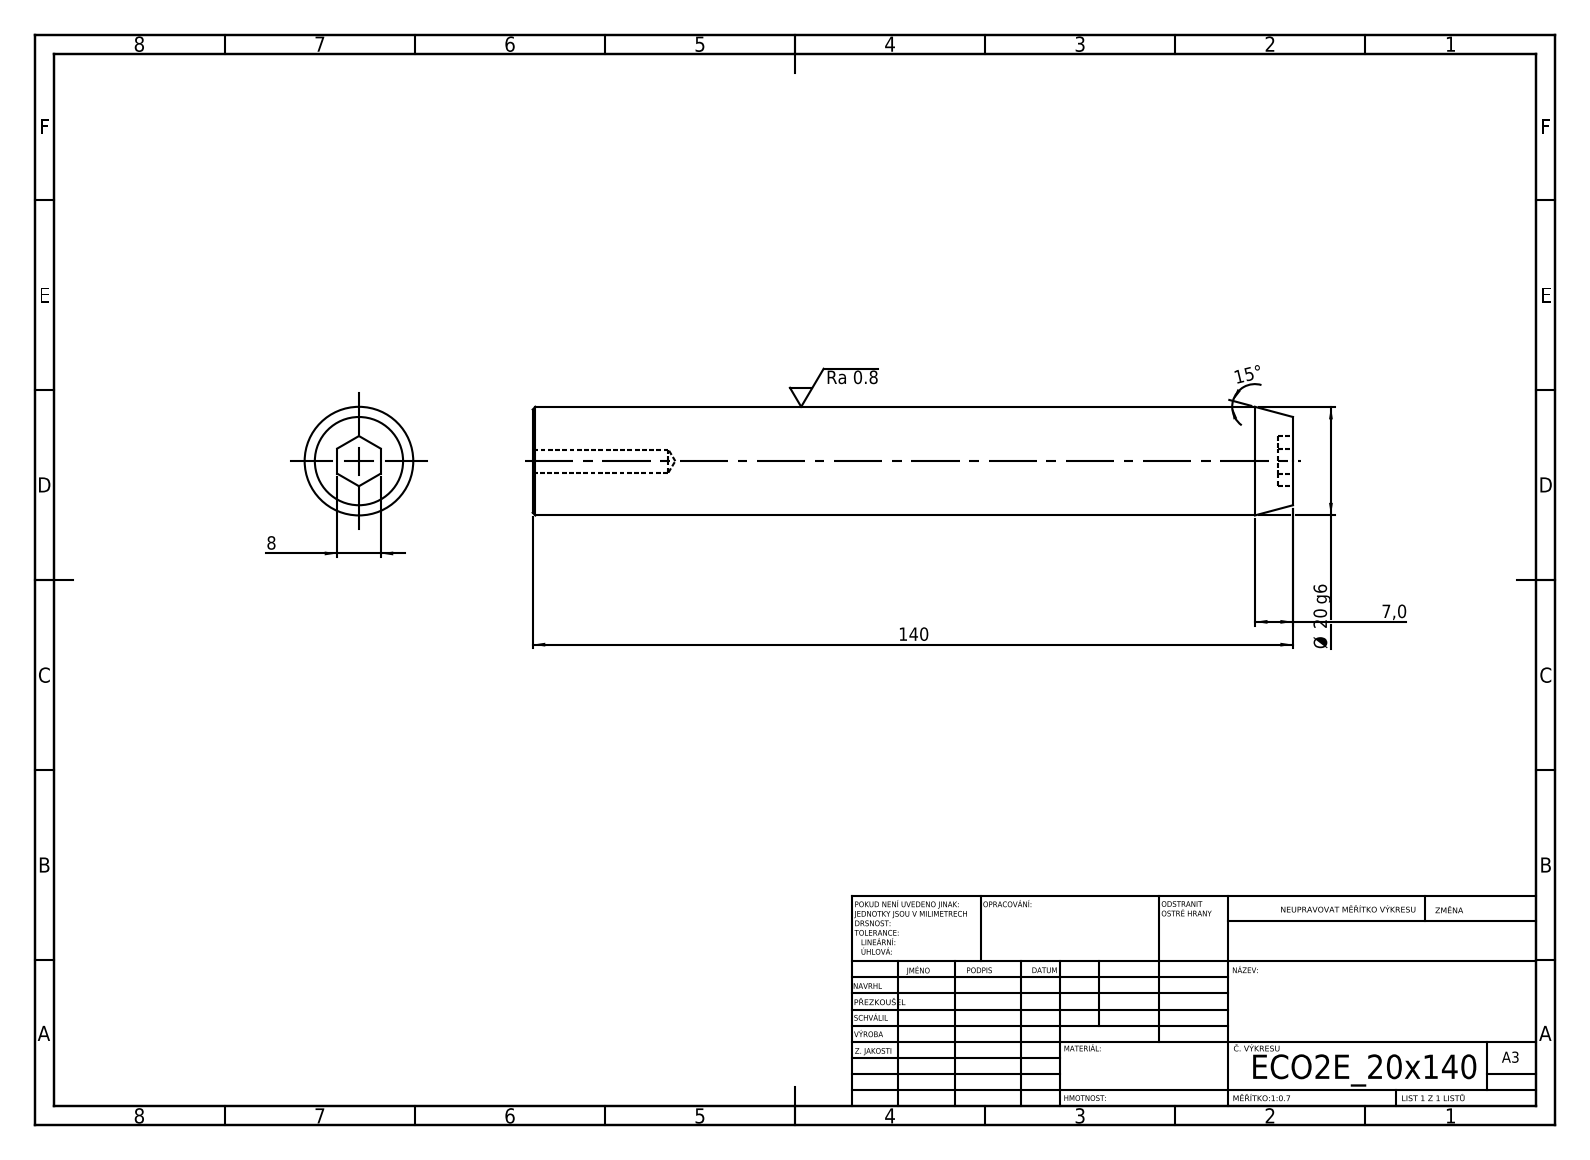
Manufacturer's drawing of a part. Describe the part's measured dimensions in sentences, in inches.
Its 3-D file was written by "SolidWorks 2019 (CONFIG_CONTROL_DESIGN)". It is 1 solid with 19 faces: 9 planar, 4 cylindrical and 6 other. Overall it measures 5.512 by 0.787 by 0.787 inches. Its volume is 2.629 cubic inches and its surface area 15.01 square inches. Round holes: 1 of diameter 0.165. Round bosses or shafts: 1 of diameter 0.787. The main face-to-face distances are 5.512, 0.11, 5.402, 0.315.
